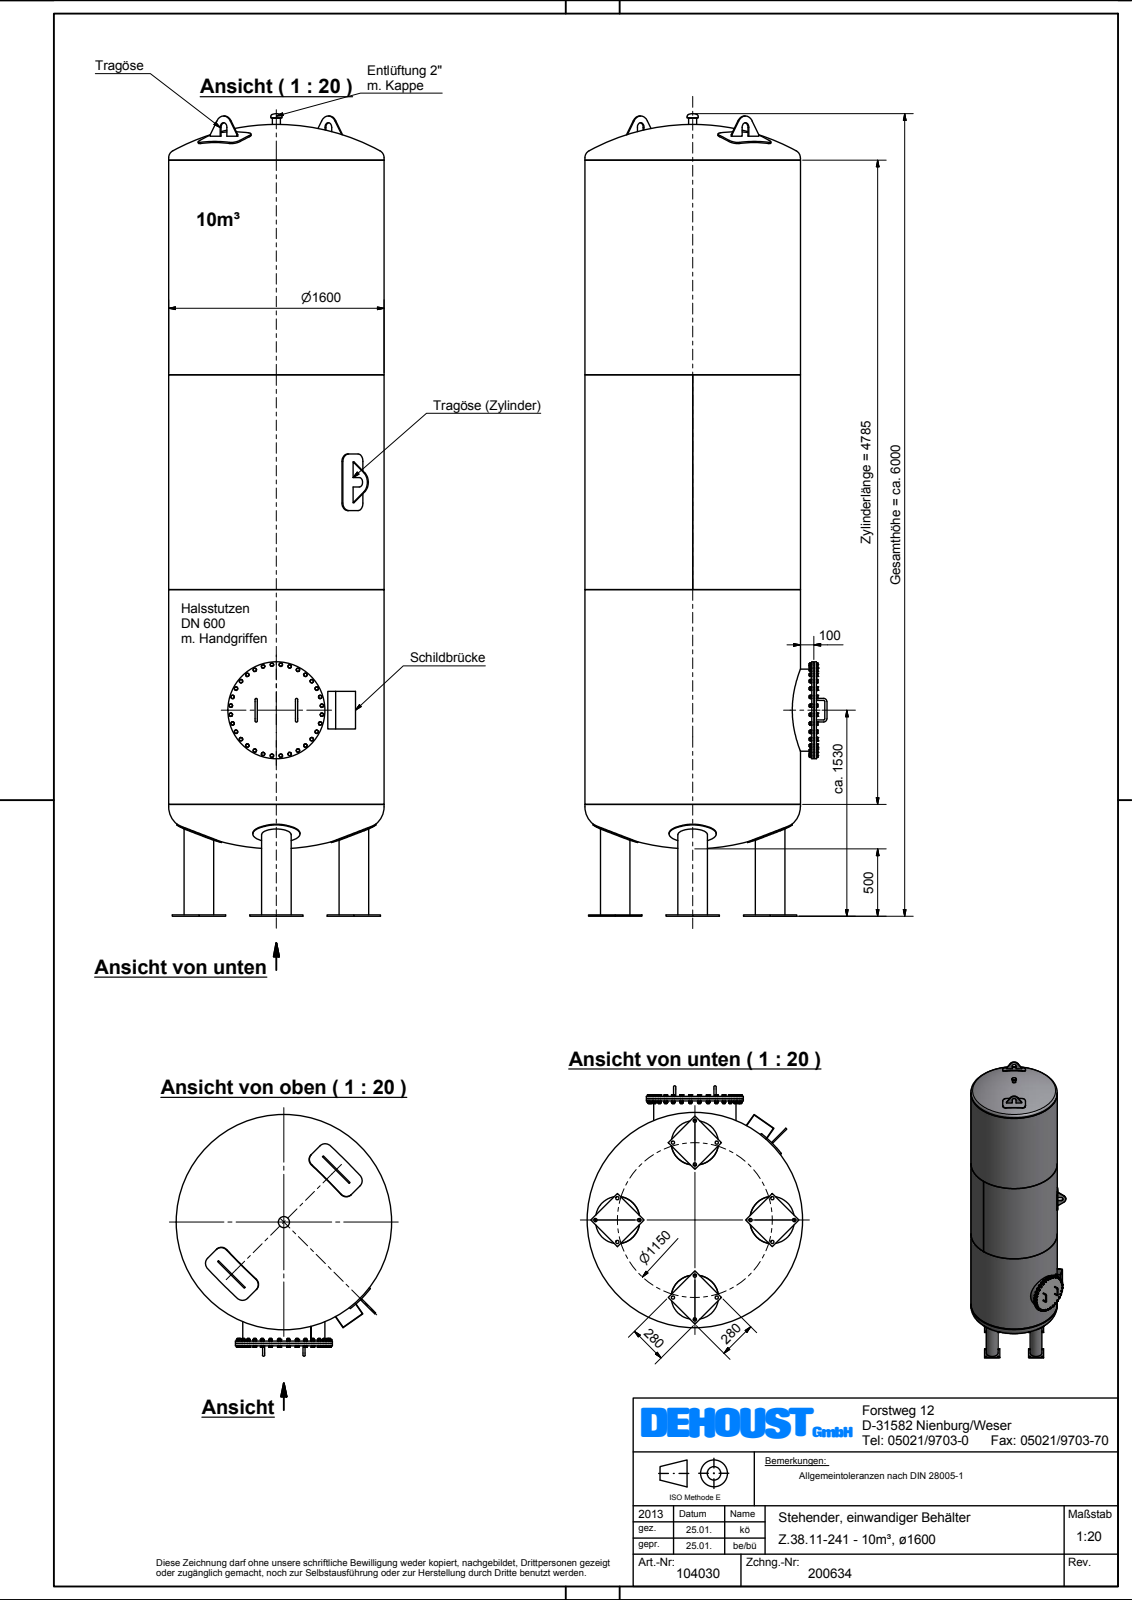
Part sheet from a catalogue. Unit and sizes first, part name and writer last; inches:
Units: inches
Overall size (bounding box): 234.667 × 70.748 × 62.992
Round holes (diameter × count): ⌀8.232 ×4, ⌀23.543 ×1, ⌀62.598 ×1
Round bosses / shafts (diameter × count): ⌀0.63 ×38, ⌀0.886 ×32, ⌀13.78 ×4, ⌀8.626 ×4, ⌀62.992 ×1, ⌀28.346 ×1, ⌀25.984 ×1, ⌀24.016 ×1
Partial cylindrical surfaces — rounded edges, fillets, slot ends (radius × count): R2.205 ×12, R1.378 ×3, R3.346 ×3, R31.89 ×1
Main face-to-face distances: 1.378, 0.394, 32.68, 32.286, 0.63, 0.748, 0.118, 0.115, 21.631, 22.024
Hole centre spacings: 22.638, 32.015, 45.276
Volume: 37 260 in³ · Surface area: 98 150 in²
Bodies: 2 solids, 1081 faces (614 planar, 153 cylindrical, 314 other)
Part name (STEP PRODUCT): Beh\S\dlter_Z-38_11-241_1600_010_KV
STEP written by: Autodesk Inventor 2012 (AUTOMOTIVE_DESIGN)
